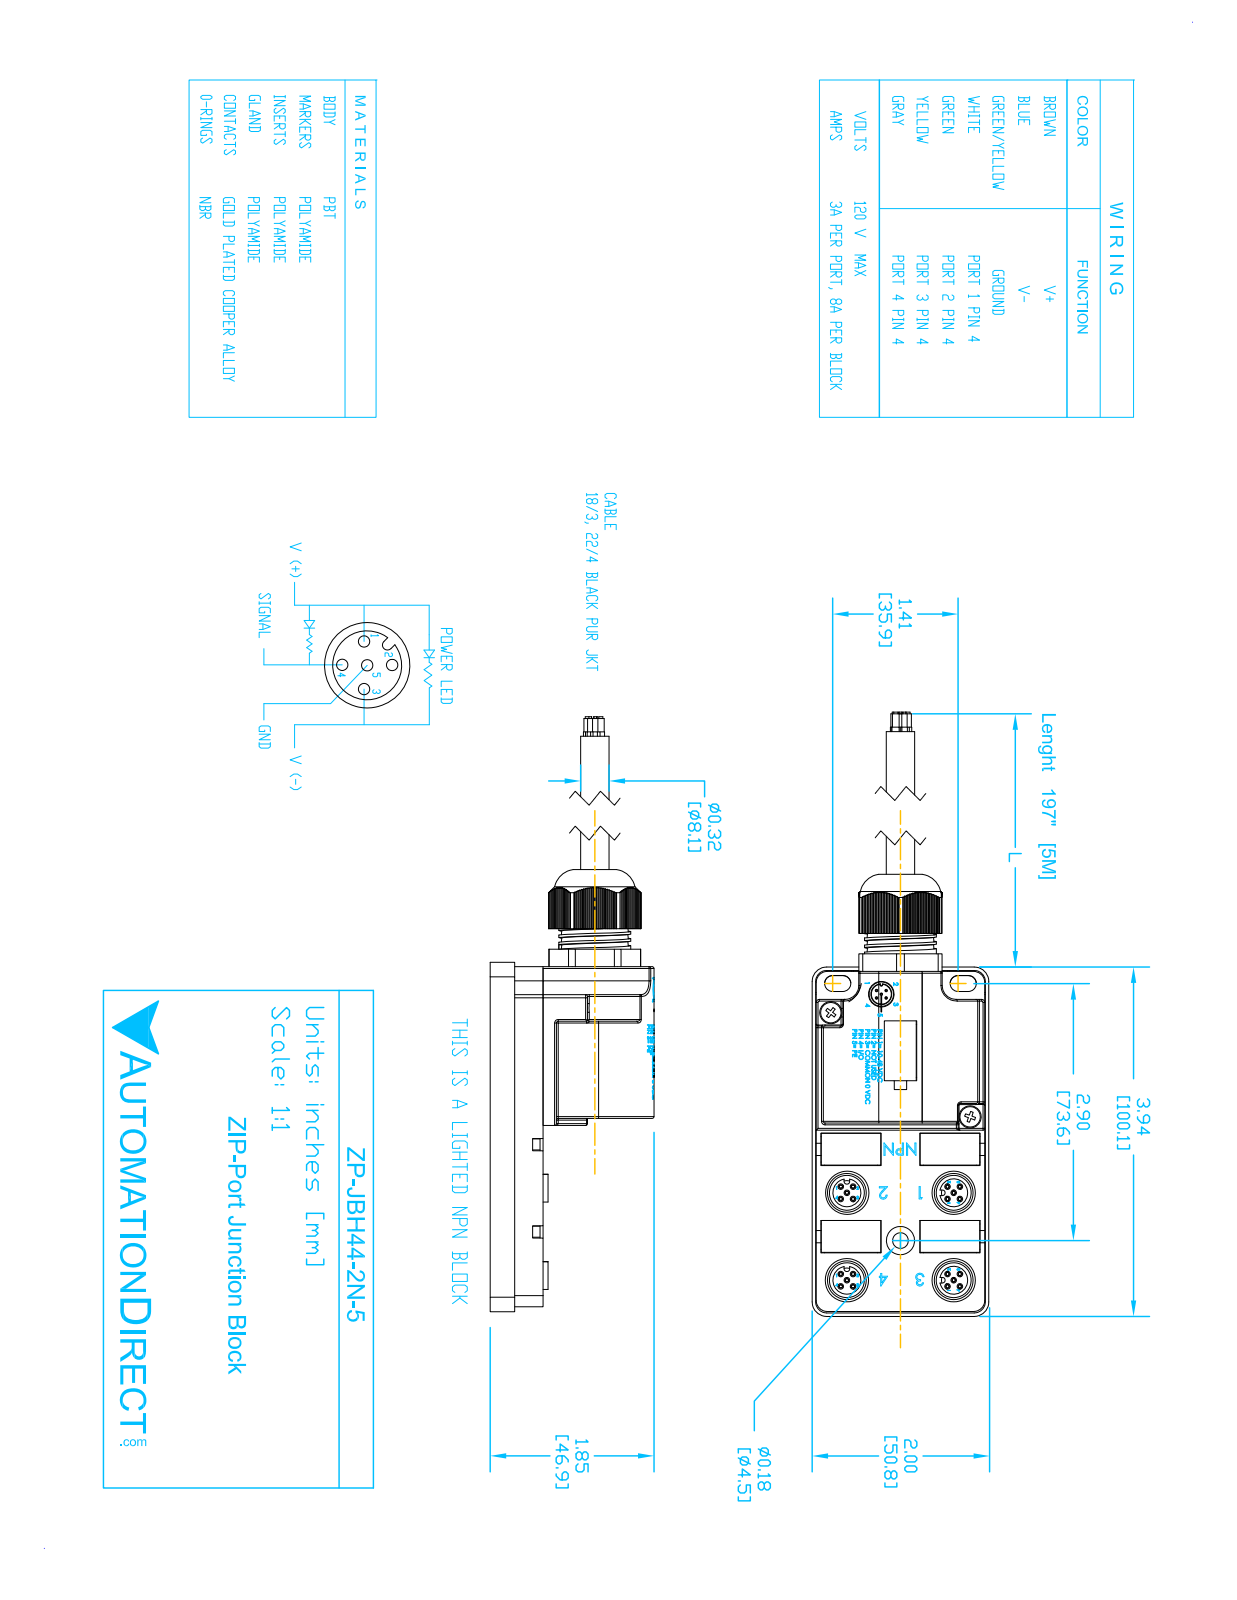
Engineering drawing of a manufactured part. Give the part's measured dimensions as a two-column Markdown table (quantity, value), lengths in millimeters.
| quantity | value |
| --- | --- |
| part name | ZP-JBH45-2P-ZZ |
| STEP written by | SolidWorks 2016 (AUTOMOTIVE_DESIGN) |
| units | millimeters |
| bodies | 8 solids, 1071 faces (640 planar, 269 cylindrical, 162 other) |
| overall size | 175.01 × 50.57 × 46.89 |
| volume | 136 144 mm³ |
| surface area | 31 283 mm² |
| round holes (diameter × count) | 1.09 × 20, 1.6 × 20, 11.1 × 4, 12.4 × 4, 6.35 × 2, 6.6 × 1, 8.08 × 1, 9.4 × 1, 12.45 × 1, 15.16 × 1 |
| round bosses / shafts (diameter × count) | 8 × 3, 20.57 × 1, 20 × 1, 8.76 × 1, 8 × 1 |
| partial cylindrical surfaces (radius × count) | 0.51 × 34, 2.29 × 8, 0.8 × 4, 4.17 × 4, 7.9 × 4, 0.89 × 2, 3.2 × 2, 3.97 × 2 |
| main face-to-face distances | 15.14, 43.44, 48.26, 1, 0.89, 14.14, 3.19, 47.38, 1.16, 49.42 |
| hole center spacings | 2.5, 3.54, 30.57, 23.34, 28.85, 30.77, 32.39, 25.04 |
